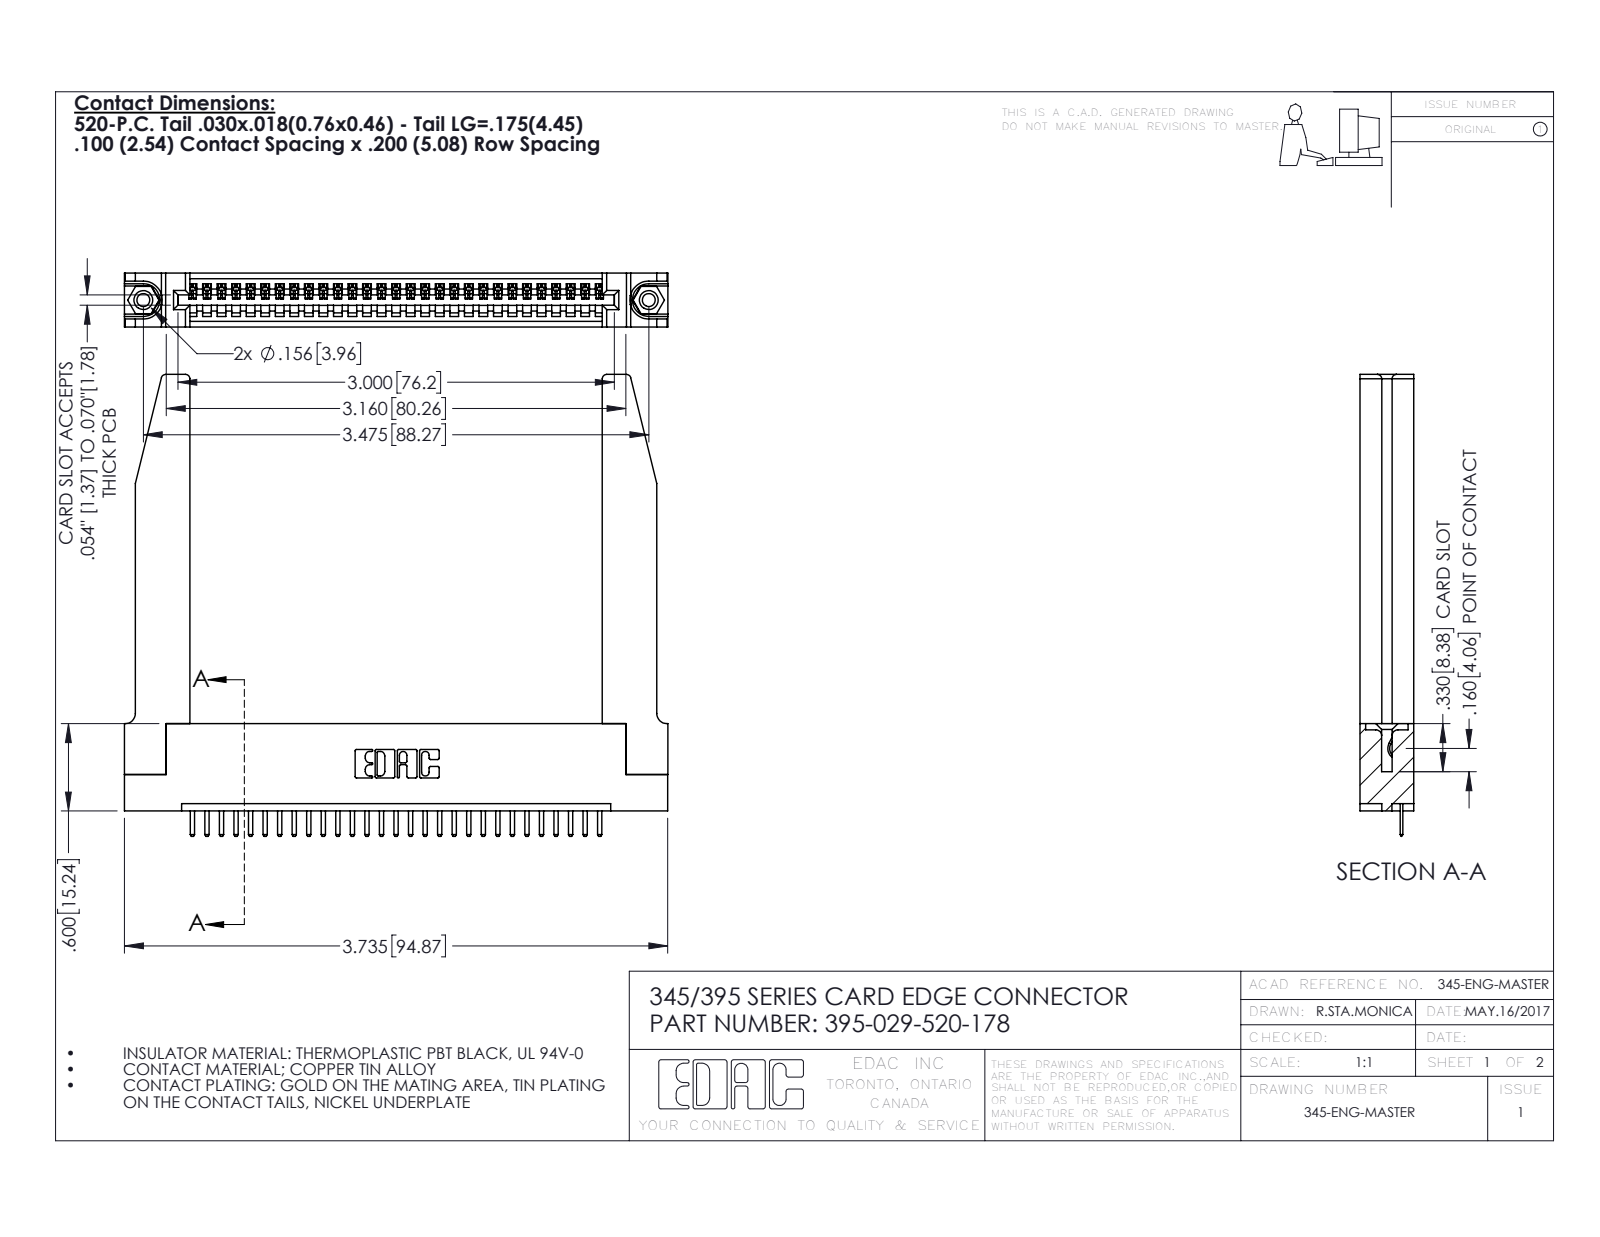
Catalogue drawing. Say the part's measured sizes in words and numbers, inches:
The part is named "395-029-520-178; 345-220-078_345-220-078; 345-250-001_345-250-001-102; 345 Part_Flush Mounting Lugs - 0.156 Dia-TH (+1 more)". Its 3-D file was written by "SolidWorks 2016 (CONFIG_CONTROL_DESIGN)". It is 34 solids with 2158 faces: 1440 planar, 666 cylindrical and 52 other. Overall it measures 3.736 by 3.175 by 0.37 inches. Its volume is 1.013 cubic inches and its surface area 28.09 square inches. Round holes: 2 of diameter 0.089, 2 of diameter 0.125, 2 of diameter 0.156, 1 of diameter 0.064. Round bosses or shafts: 2 of diameter 0.155. Partial cylindrical surfaces (rounded edges, fillets, slot ends): 60 of radius 0.01, 58 of radius 0.006, 22 of radius 0.01, 8 of radius 0.03, 6 of radius 0.007, 6 of radius 0.031, 3 of radius 0.026, 2 of radius 0.031. The main face-to-face distances are 0.37, 0.072, 0.298, 0.2, 0.098, 0.272, 0.025, 0.148, 0.15, 0.225. The hole center spacings are 0.27, 3.24, 3.475.
